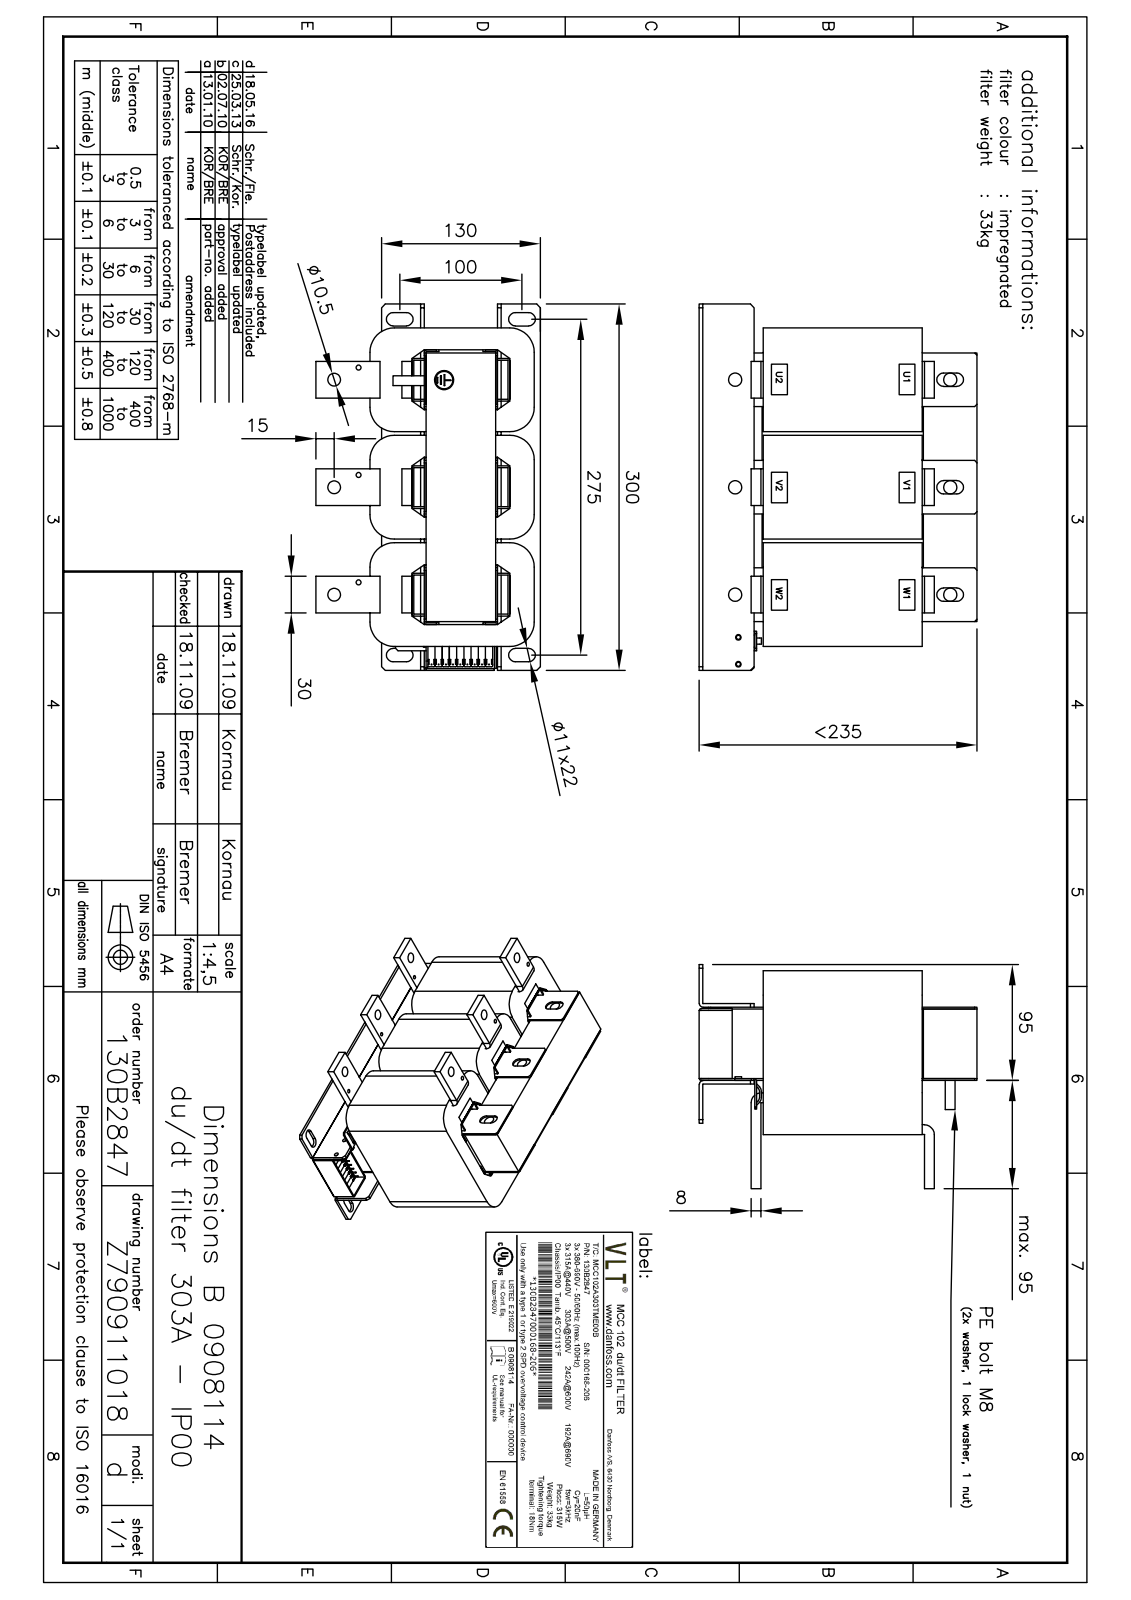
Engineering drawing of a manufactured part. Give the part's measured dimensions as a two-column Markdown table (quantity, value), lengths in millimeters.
| quantity | value |
| --- | --- |
| part name | #700-1261; M8x80-DIN84; #700-1260; plain washer grade a_din_Washer DIN 125 - A 4.3 (+8 more) |
| STEP written by | SolidWorks 2014 (AUTOMOTIVE_DESIGN) |
| units | millimeters |
| bodies | 91 solids, 1273 faces (853 planar, 185 cylindrical, 235 other) |
| overall size | 300 × 233.8 × 173 |
| volume | 6 036 000 mm³ |
| surface area | 1 029 000 mm² |
| round holes (diameter × count) | 3.7 × 6, 6.8 × 6, 8 × 6, 8.4 × 6, 10 × 6, 11 × 6, 4.1 × 5, 4.5 × 4, 4.3 × 3, 10.5 × 3, 4 × 2, 5.76 × 1 |
| round bosses / shafts (diameter × count) | 24 × 6, 16 × 6, 13 × 6, 8 × 5, 7.6 × 5, 9 × 3, 4 × 3, 6 × 2 |
| partial cylindrical surfaces (radius × count) | 5.5 × 16, 20 × 12, 0.1 × 7, 1.6 × 5, 4 × 4, 1 × 2, 8.1 × 2 |
| main face-to-face distances | 58, 1.5, 88, 27.6, 44, 55.2, 26.4, 21, 65, 56.5 |
| hole center spacings | 88, 22.36, 176, 80.52, 100.02, 202.43, 20, 182.3 |
